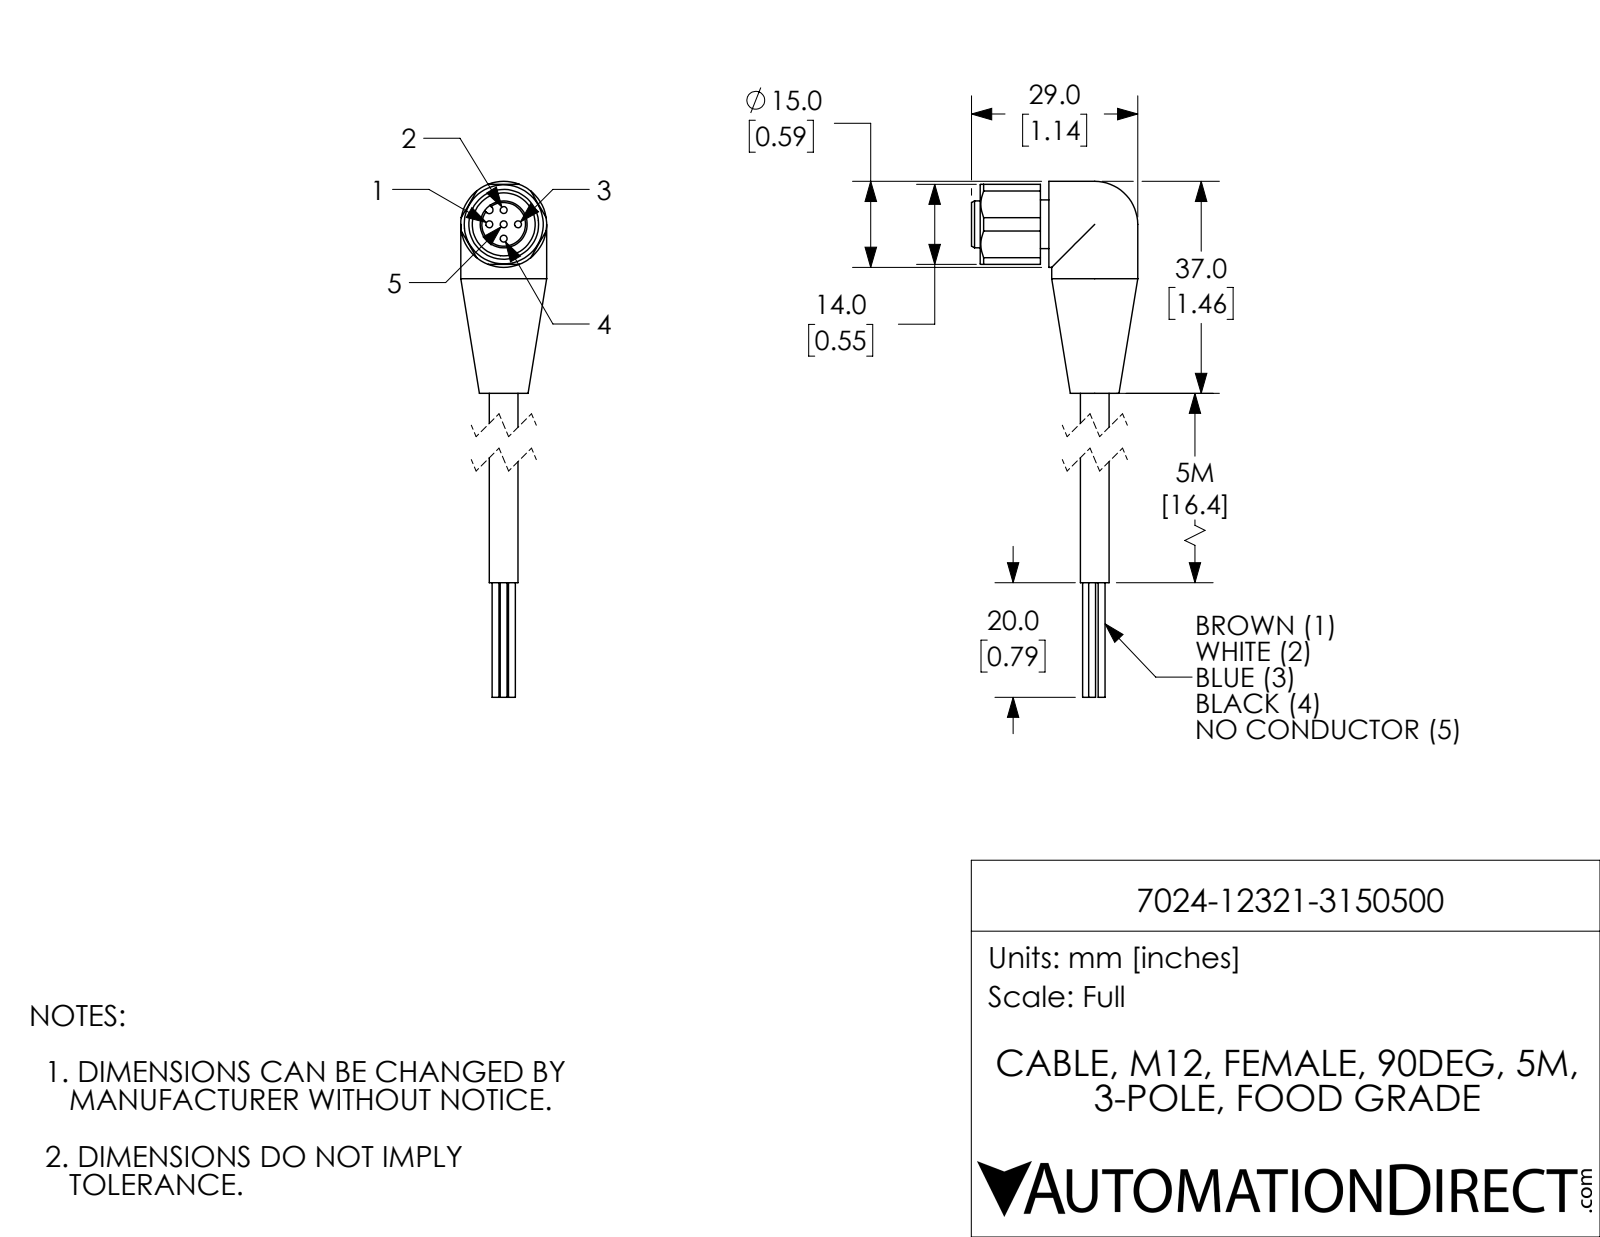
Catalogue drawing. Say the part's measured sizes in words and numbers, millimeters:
The part is named "7024-12321-3150500". Its 3-D file was written by "SolidWorks 2018 (AUTOMOTIVE_DESIGN)". It is 1 solid with 76 faces: 26 planar, 40 cylindrical and 10 other. Overall it measures 87 by 29 by 15 millimeters. Its volume is 7 424 cubic millimeters and its surface area 3 961 square millimeters. Round holes: 5 of diameter 1.2, 1 of diameter 11. Round bosses or shafts: 5 of diameter 1.2, 2 of diameter 15, 1 of diameter 8.5, 1 of diameter 8.2, 1 of diameter 5. Partial cylindrical surfaces (rounded edges, fillets, slot ends): 1 of radius 0.65. The main face-to-face distances are 14, 1.5, 12, 4.5, 3, 13.5, 9, 22.5, 36.5, 10.5. The hole center spacings are 2.5, 3.54, 5.
